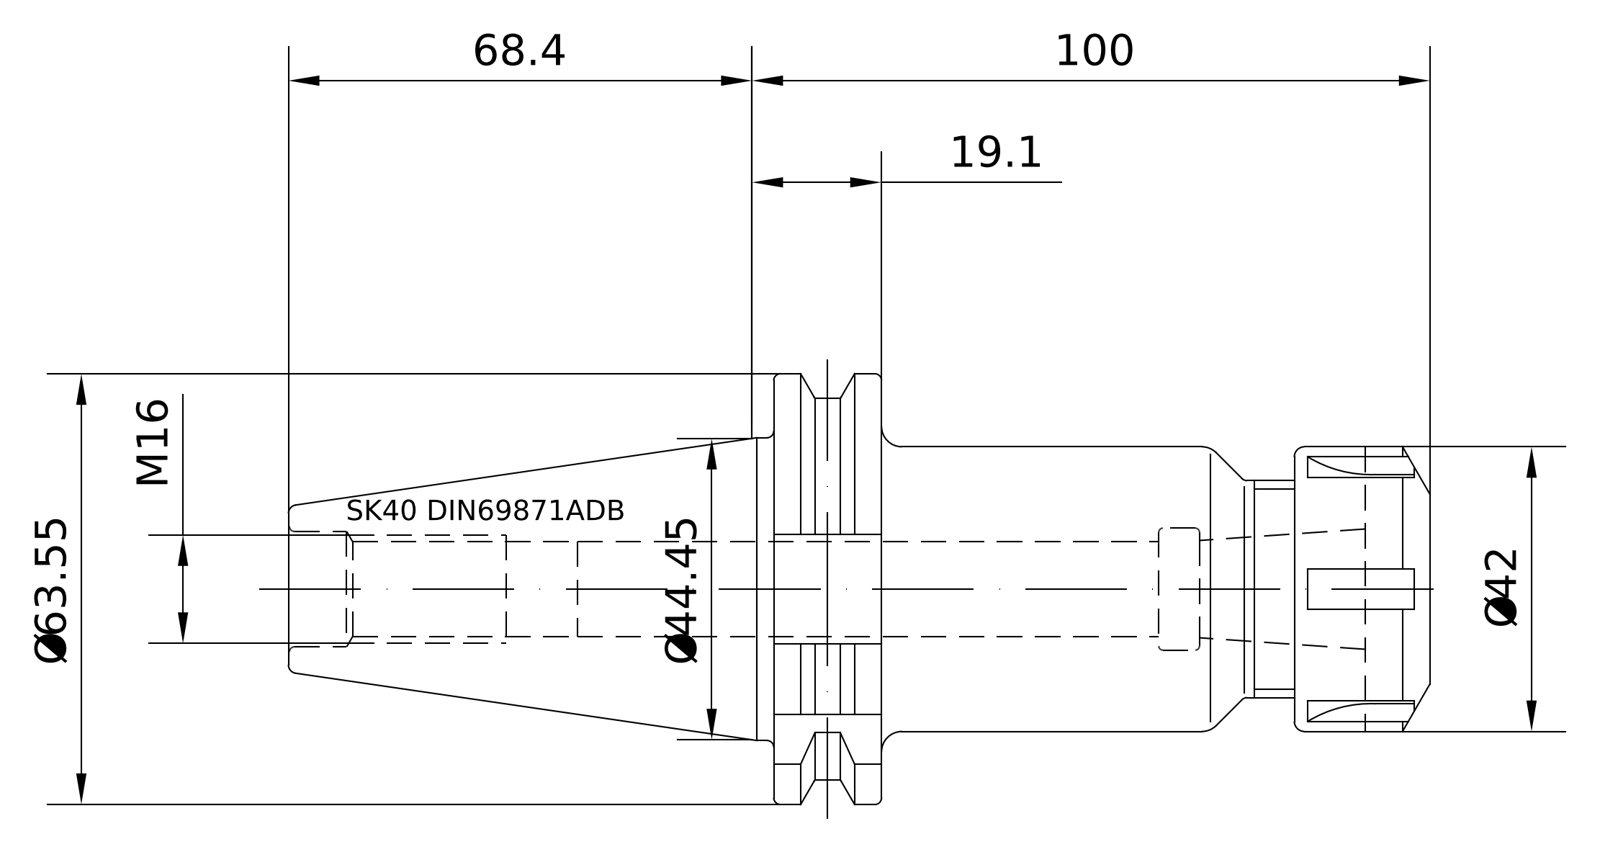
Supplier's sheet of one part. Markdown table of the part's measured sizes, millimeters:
| quantity | value |
| --- | --- |
| part name | 40-321-25; 83-912-25; 40-321-25_ASM |
| STEP written by | PRO/ENGINEER BY PARAMETRIC TECHNOLOGY CORPORATION, 2010430 (CONFIG_CONTROL_DESIGN) |
| units | millimeters |
| bodies | 2 solids, 143 faces (41 planar, 28 cylindrical, 74 other) |
| overall size | 168.25 × 63.52 × 61.42 |
| volume | 202 396 mm³ |
| surface area | 35 725 mm² |
| round holes (diameter × count) | 13.84 × 1, 17.01 × 1, 17.5 × 1, 18 × 1 |
| round bosses / shafts (diameter × count) | 43.75 × 1, 42 × 1, 32 × 1, 16.01 × 1 |
| partial cylindrical surfaces (radius × count) | 1.35 × 1, 28 × 1, 31.76 × 1 |
| main face-to-face distances | 76.8, 15.85, 60.95, 96.8, 80.95, 20, 84.8, 68.95, 8, 12 |
